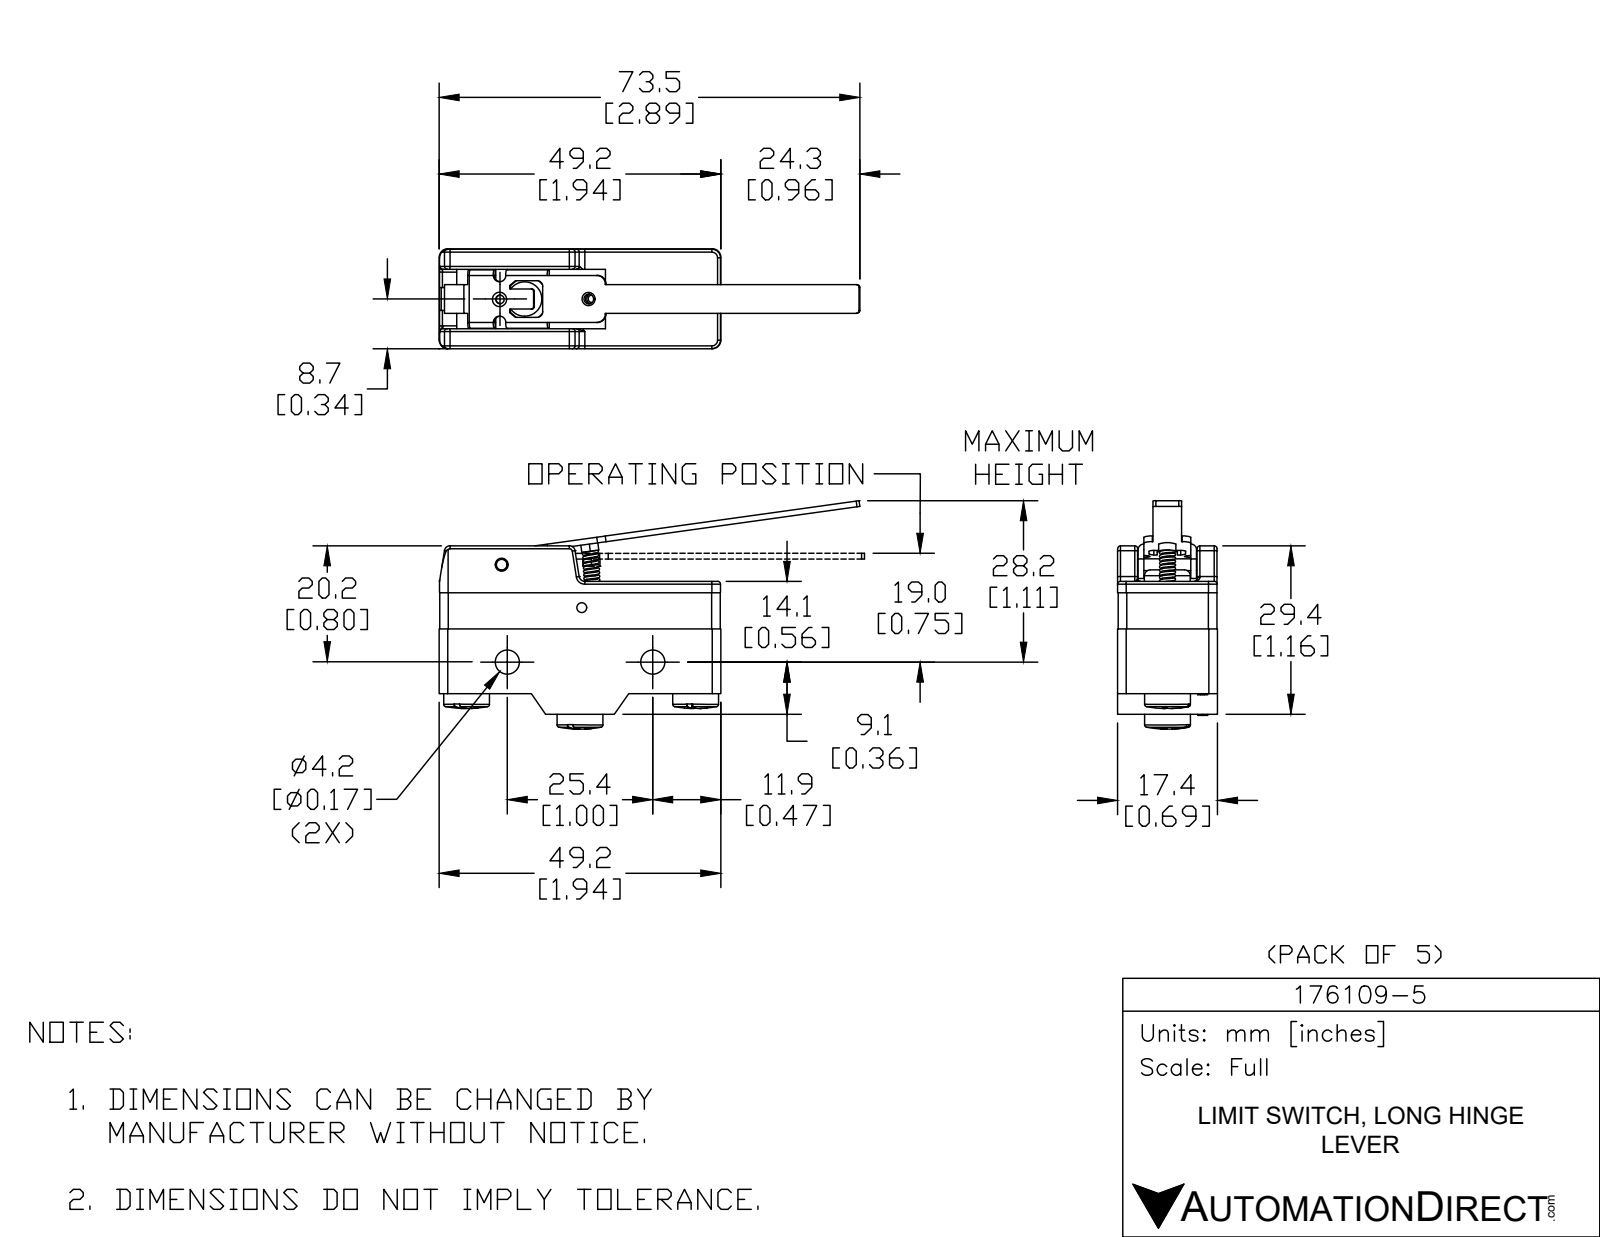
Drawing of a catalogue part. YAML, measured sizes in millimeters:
part_name: "176-MS (Screw Terminal)-Long Hinge Lever"
step_written_by: "SolidWorks 2018 (AUTOMOTIVE_DESIGN)"
units: millimeters
bodies: {solids: 3, faces: 580, planar: 271, cylindrical: 119, other: 190}
overall_size: [73.5, 39.9, 17.4]
volume: 17830
surface_area: 9994
round_holes:
  - {diameter: 6, count: 3}
  - {diameter: 1.7, count: 2}
  - {diameter: 2, count: 2}
  - {diameter: 4.2, count: 2}
  - {diameter: 1.5, count: 1}
round_bosses_or_shafts:
  - {diameter: 8, count: 4}
  - {diameter: 3.8, count: 3}
  - {diameter: 2.1, count: 1}
  - {diameter: 2, count: 1}
  - {diameter: 1.8, count: 1}
partial_cylinders:
  - {radius: 0.5, count: 21}
  - {radius: 1.5, count: 14}
  - {radius: 0.3, count: 12}
  - {radius: 1, count: 7}
  - {radius: 2.9, count: 3}
  - {radius: 0.4, count: 2}
  - {radius: 0.8, count: 2}
  - {radius: 1.1, count: 2}
face_to_face_distances: [1, 17.3, 17.4, 17.6, 2, 19.6, 3.5, 13.9, 17.3, 13.8]
hole_center_spacings: [9.7, 10.1, 15.6, 15.7, 15.8, 16.1, 17, 19.8]
